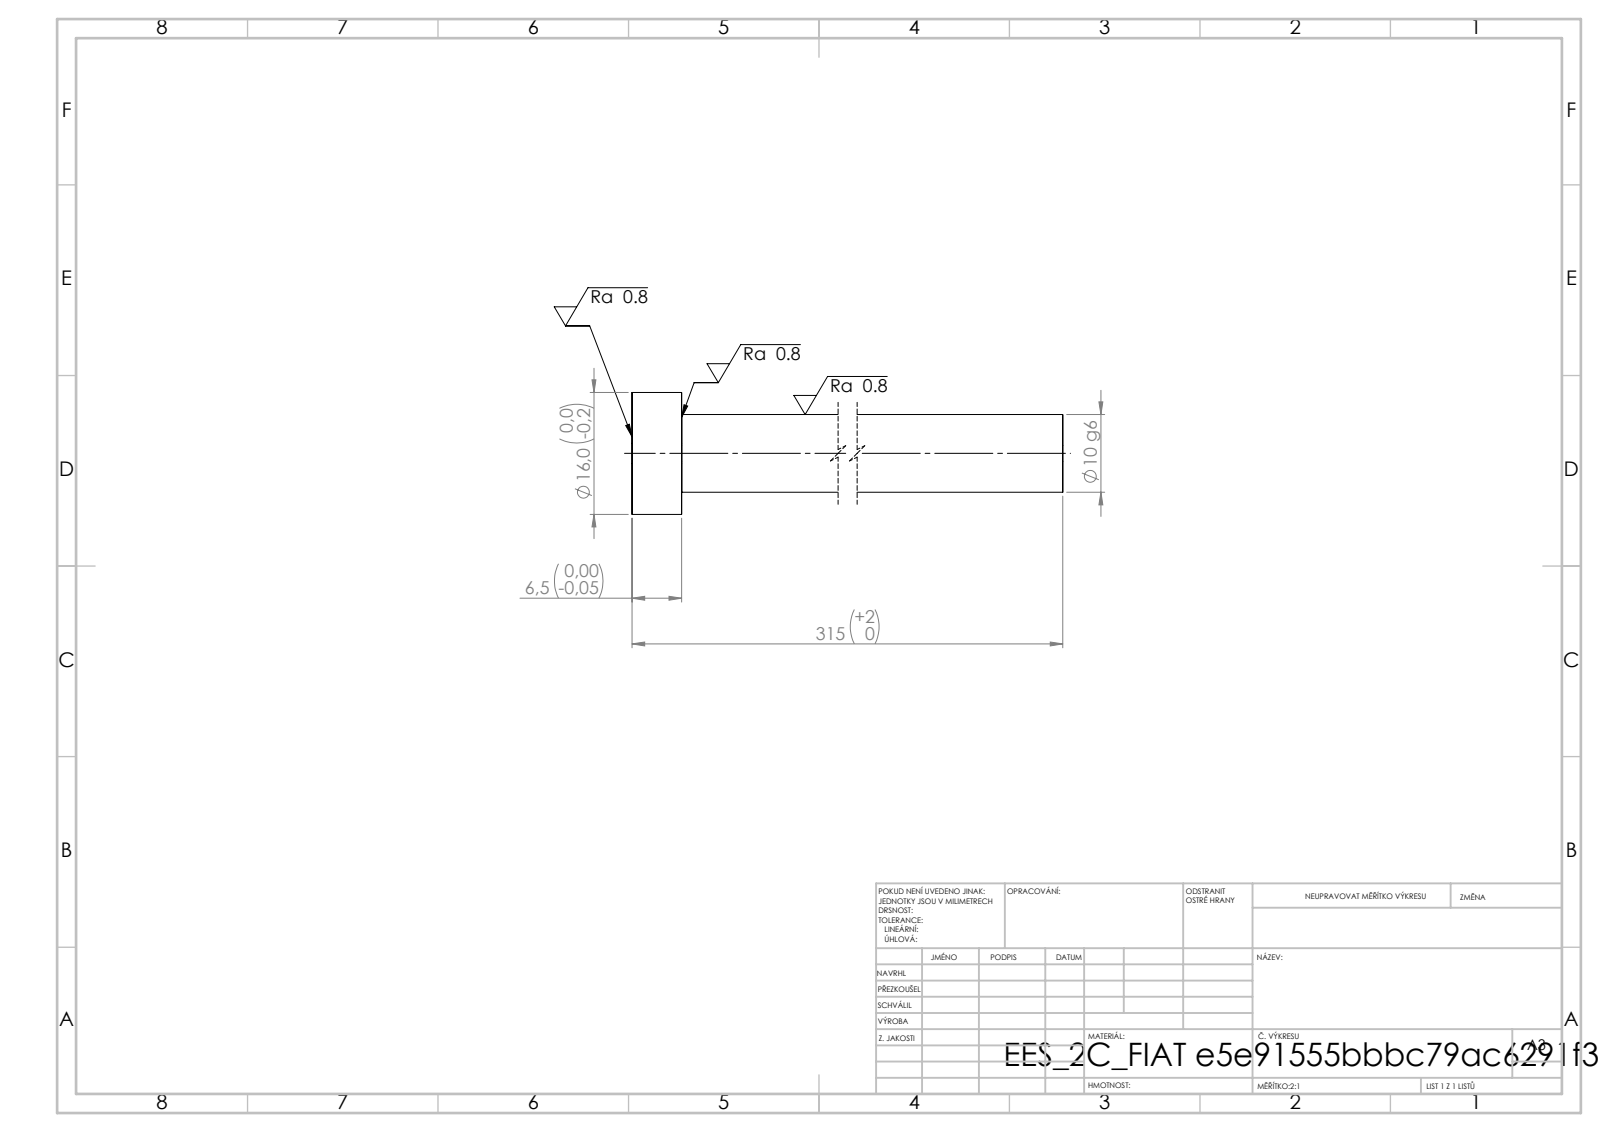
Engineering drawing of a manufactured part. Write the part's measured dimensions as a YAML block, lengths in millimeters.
step_written_by: "SolidWorks 2019 (CONFIG_CONTROL_DESIGN)"
units: millimeters
bodies: {solids: 1, faces: 7, planar: 3, cylindrical: 4, other: 0}
overall_size: [315, 16, 16]
volume: 26515
surface_area: 10614
round_bosses_or_shafts:
  - {diameter: 16, count: 1}
  - {diameter: 10.2, count: 1}
face_to_face_distances: [6.5, 315, 308.5]
